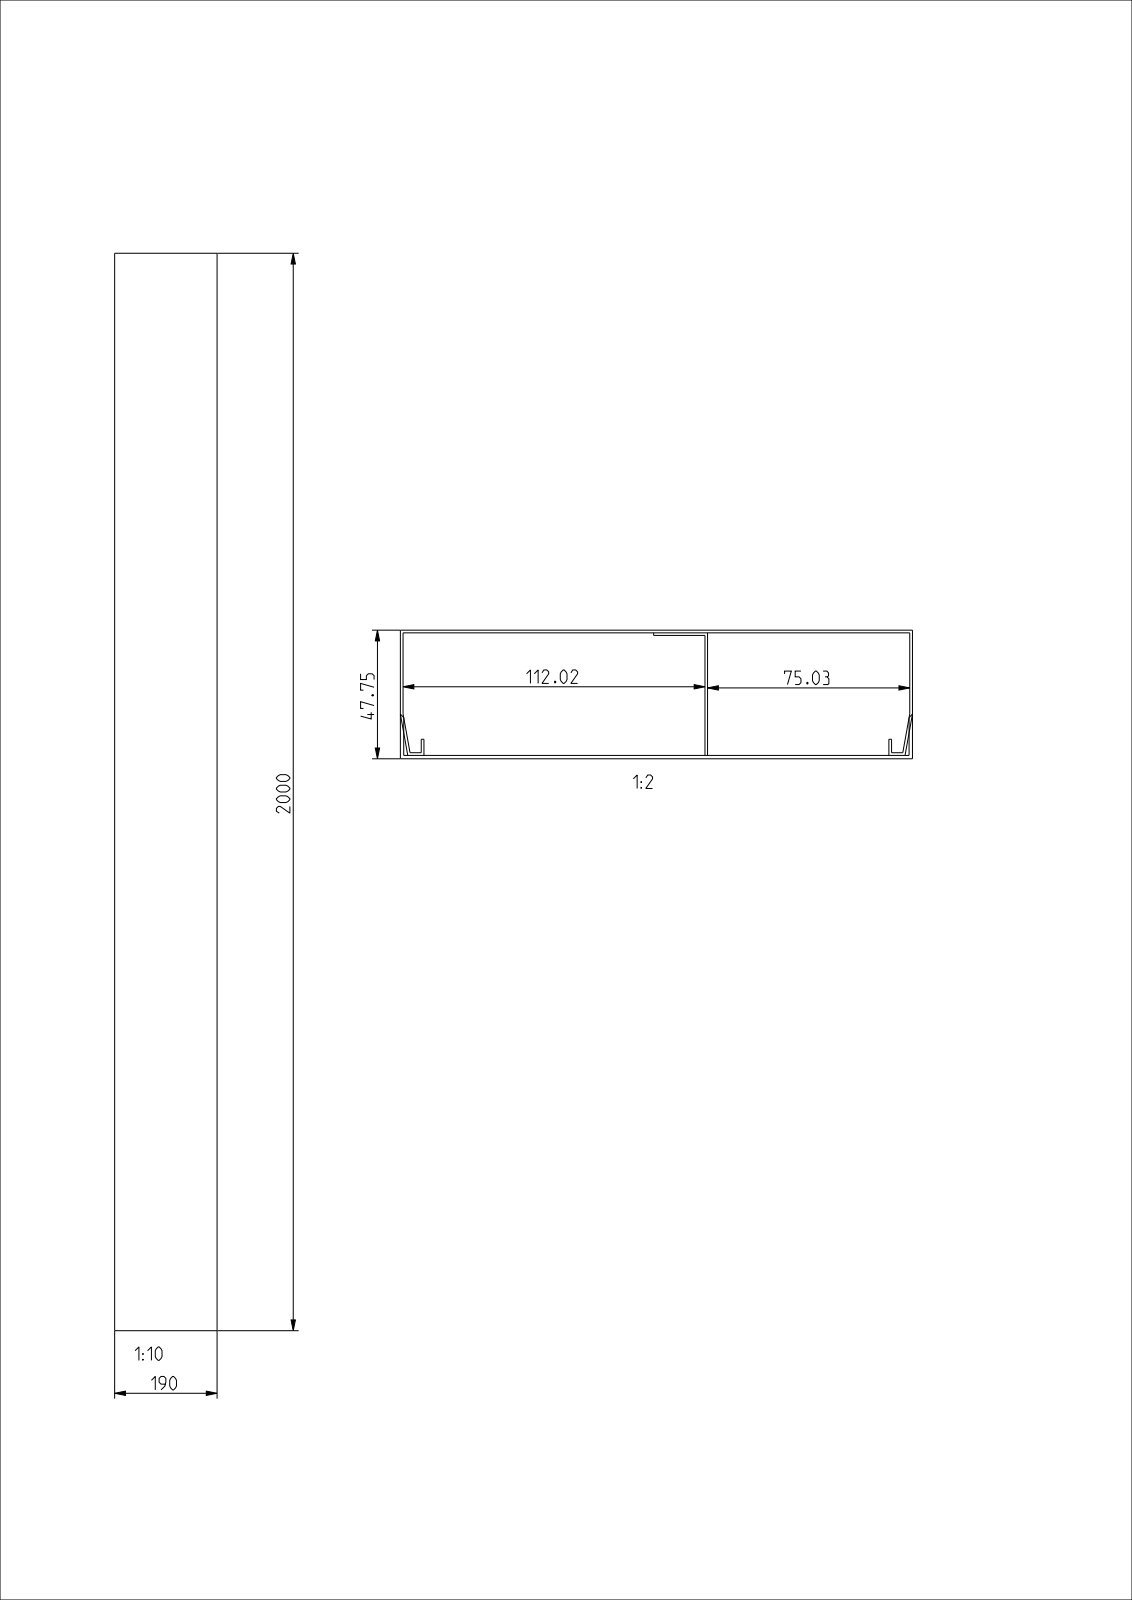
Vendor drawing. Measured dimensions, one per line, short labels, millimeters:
name: UK190482KUN_UNTERTEIL; UK190482KUN_OBERTEIL; UK190482KUN_ASM
written by: CREO PARAMETRIC BY PTC INC, 2022024 (AUTOMOTIVE_DESIGN)
unit: mm
bodies: 2 solids, 39 faces (39 planar, 0 cylindrical, 0 other)
size: 2000 × 190 × 47.75
volume: 1 275 000 mm³; area: 2 278 000 mm²
face distances: 1, 1.25, 46.5, 47.75, 45.5, 46.75, 189, 190, 113.97, 76.03
